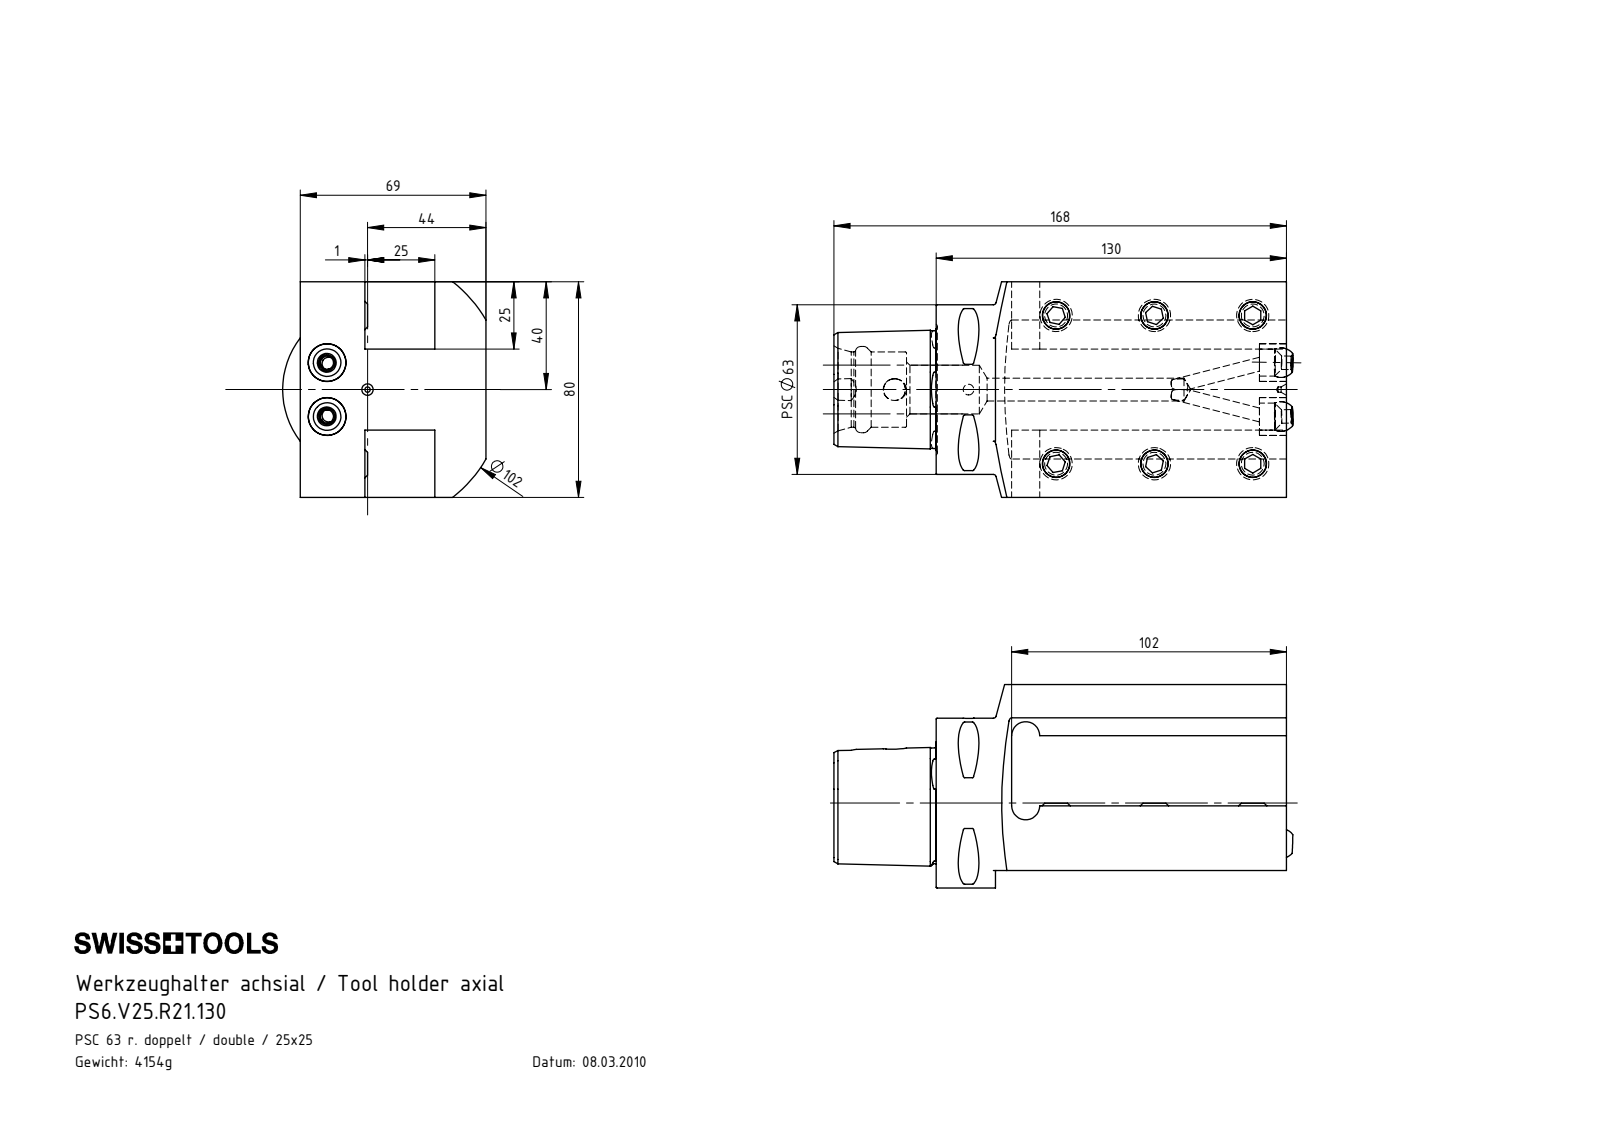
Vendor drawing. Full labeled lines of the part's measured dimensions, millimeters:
Part name (STEP PRODUCT): KU1-U14.001.012_1; PS6.V25.R21.130; KU1-U14.001.012; KU1-U14.001.012_2 (+2 more)
STEP written by: SolidWorks 2017 (AUTOMOTIVE_DESIGN)
Units: millimetres
Bodies: 11 solids, 304 faces (94 planar, 81 cylindrical, 129 other)
Overall size (bounding box): 170.81 × 80 × 75.5
Volume: 530 358 mm³ · Surface area: 83 077 mm²
Round holes (diameter × count): ⌀10.2 ×6, ⌀5 ×4, ⌀10 ×2, ⌀14 ×2, ⌀2 ×1, ⌀4 ×1, ⌀8.1 ×1, ⌀8.4 ×1, ⌀18 ×1, ⌀28 ×1, ⌀32 ×1
Round bosses / shafts (diameter × count): ⌀12 ×6, ⌀63 ×1
Partial cylindrical surfaces — rounded edges, fillets, slot ends (radius × count): R0.5 ×8, R5.2 ×2, R6 ×1, R51 ×1
Main face-to-face distances: 25, 55, 69, 19, 50, 45, 26, 24, 80, 30
Hole centre spacings: 36.5, 66.01, 55, 18.03, 42.57, 66, 73, 74.28
